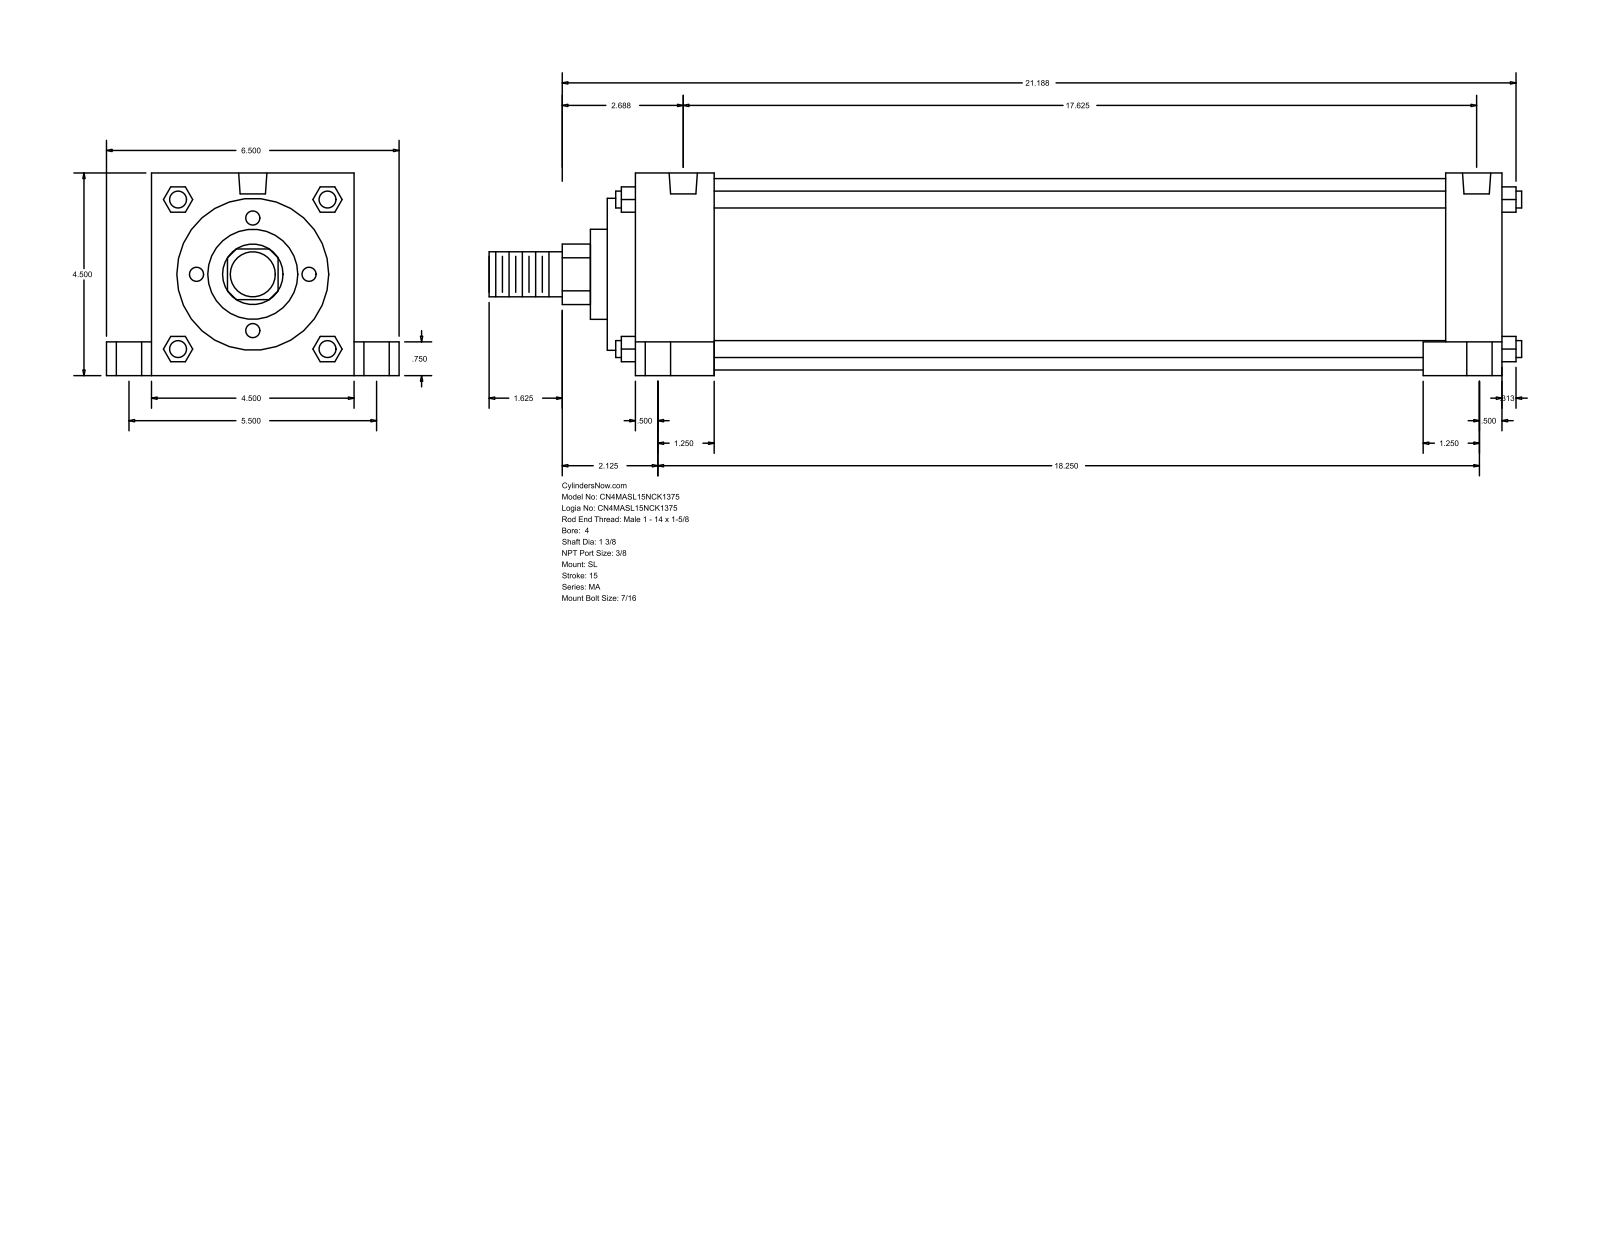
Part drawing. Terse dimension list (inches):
name: MA_SL__0400_1.375
written by: GSSL Pune (CONFIG_CONTROL_DESIGN)
unit: in
bodies: 0 solids, 150 faces (113 planar, 37 cylindrical, 0 other)
size: 22.937 × 6.5 × 4.5
holes: 4× ⌀0.437, 4× ⌀0.563, 4× ⌀0.813, 2× ⌀0.627
bosses: 4× ⌀0.375, 1× ⌀4.25, 1× ⌀3.375, 1× ⌀2, 1× ⌀1.375, 1× ⌀1
rounds: 1× R0.672
face distances: 4.5, 19.25, 0.625, 19.875, 2.375, 1.75, 17.5, 18.625, 18, 16.25
hole spacings: 2.751, 2.761, 2.807, 2.85, 5.5, 17.25, 17.714, 17.9
